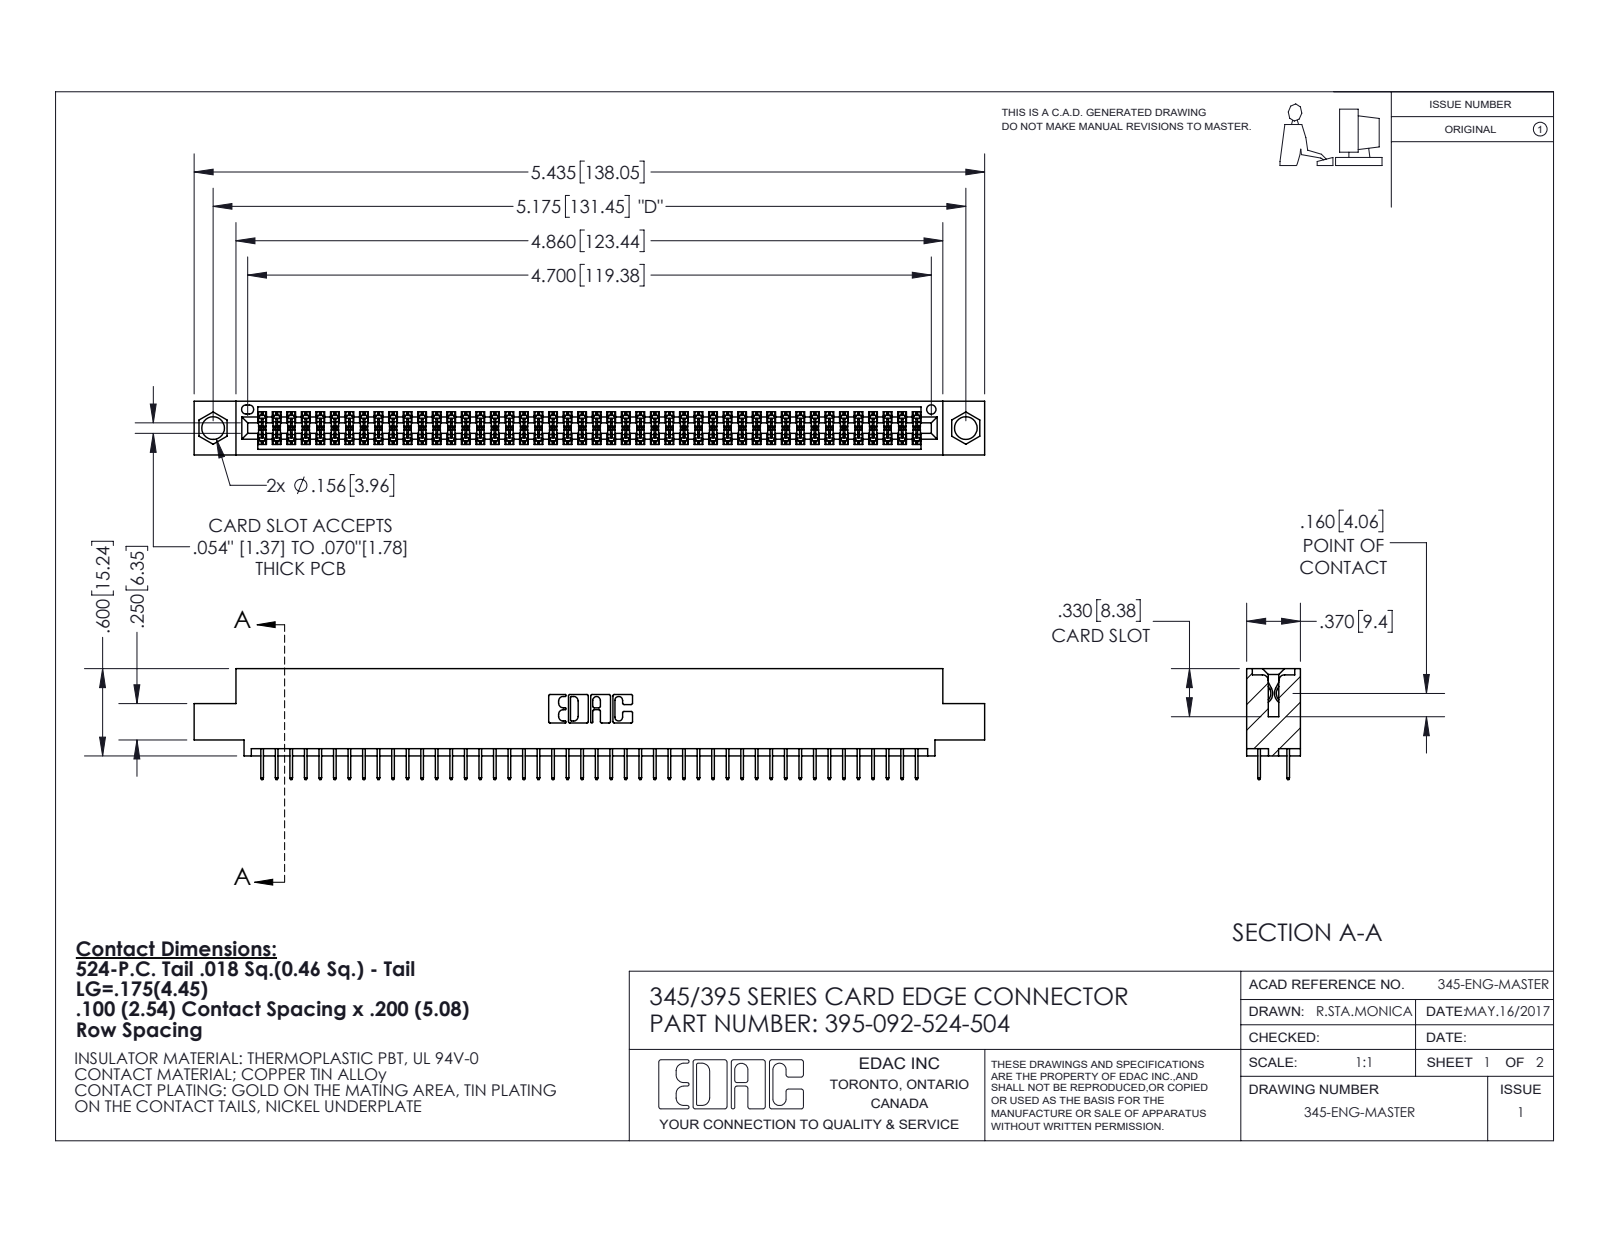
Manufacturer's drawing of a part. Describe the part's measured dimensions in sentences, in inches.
The part is named "345 Part_0.110 Offset - 0.156 Dia-TI; 395-092-524-504; 345-292-001_345-293-124". Its 3-D file was written by "SolidWorks 2020 (CONFIG_CONTROL_DESIGN)". It is 93 solids with 5112 faces: 3686 planar, 1426 cylindrical and 0 other. Overall it measures 5.435 by 0.762 by 0.37 inches. Its volume is 0.801 cubic inches and its surface area 29.54 square inches. Round holes: 2 of diameter 0.156, 1 of diameter 0.064. Partial cylindrical surfaces (rounded edges, fillets, slot ends): 138 of radius 0.006, 22 of radius 0.01, 6 of radius 0.007, 6 of radius 0.031, 3 of radius 0.026, 2 of radius 0.014, 2 of radius 0.019, 2 of radius 0.022. The main face-to-face distances are 0.072, 0.298, 0.2, 0.37, 0.098, 0.272, 0.025, 0.225, 0.072, 0.175. The hole center spacings are 0.27, 4.939, 5.175.
